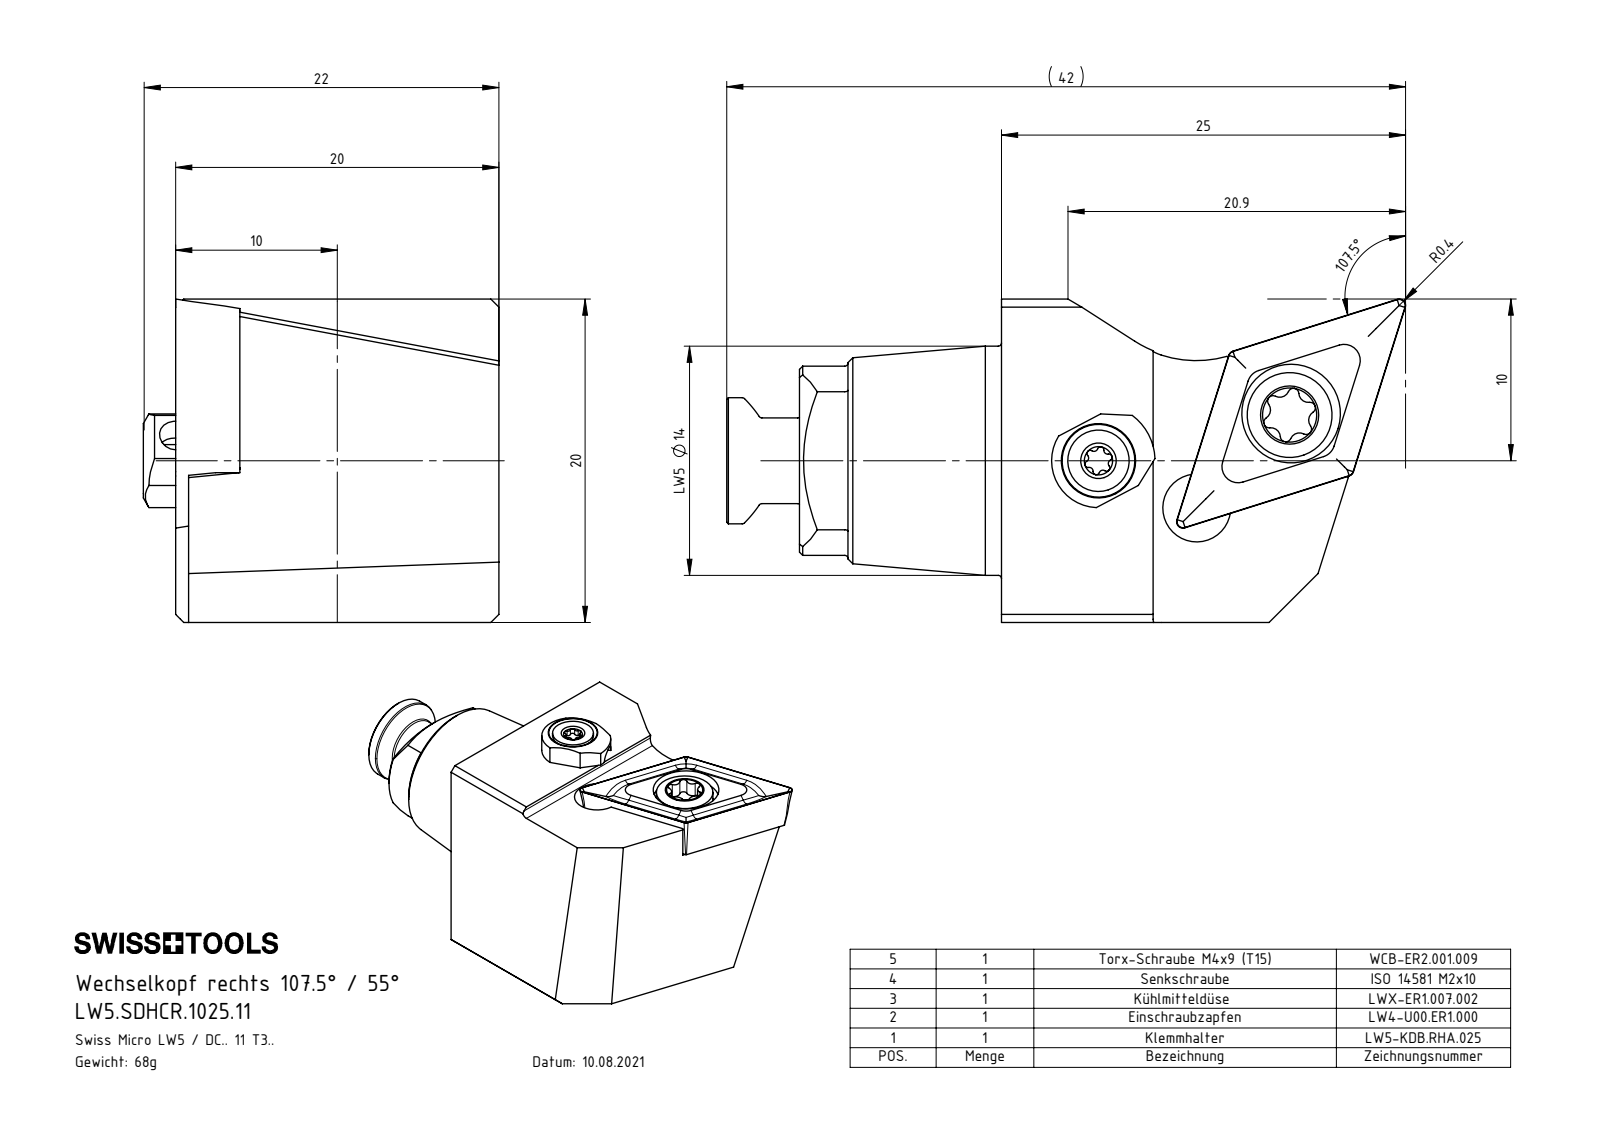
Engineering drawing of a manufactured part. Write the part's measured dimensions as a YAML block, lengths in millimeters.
part_name: "LW4-U00.ER1.000_B; LW5-KDB.RHA.025_A; ISO 14581 - M2x10; WCB-ER2.001.009_A (+3 more)"
step_written_by: "SolidWorks 2022 (CONFIG_CONTROL_DESIGN)"
units: millimeters
bodies: {solids: 6, faces: 263, planar: 70, cylindrical: 82, other: 111}
overall_size: [42.01, 22, 20]
volume: 8352
surface_area: 4335
round_holes:
  - {diameter: 2, count: 2}
  - {diameter: 1.6, count: 1}
  - {diameter: 2.5, count: 1}
  - {diameter: 3, count: 1}
  - {diameter: 3.3, count: 1}
  - {diameter: 4.2, count: 1}
  - {diameter: 4.4, count: 1}
  - {diameter: 5.5, count: 1}
  - {diameter: 6.1, count: 1}
round_bosses_or_shafts:
  - {diameter: 14.17, count: 1}
  - {diameter: 7.7, count: 1}
  - {diameter: 6, count: 1}
  - {diameter: 5.3, count: 1}
  - {diameter: 5.25, count: 1}
  - {diameter: 5, count: 1}
  - {diameter: 4, count: 1}
  - {diameter: 3.8, count: 1}
partial_cylinders:
  - {radius: 0.2, count: 8}
  - {radius: 0.24, count: 6}
  - {radius: 0.34, count: 6}
  - {radius: 0.59, count: 6}
  - {radius: 0.5, count: 1}
  - {radius: 1, count: 1}
  - {radius: 2.9, count: 1}
  - {radius: 3.5, count: 1}
face_to_face_distances: [20, 16.03, 3.97, 19.2, 3.17, 0.8, 7.5, 2, 3, 12.5]
hole_center_spacings: [6.39, 8.13, 8.26, 11.78, 11.88]
